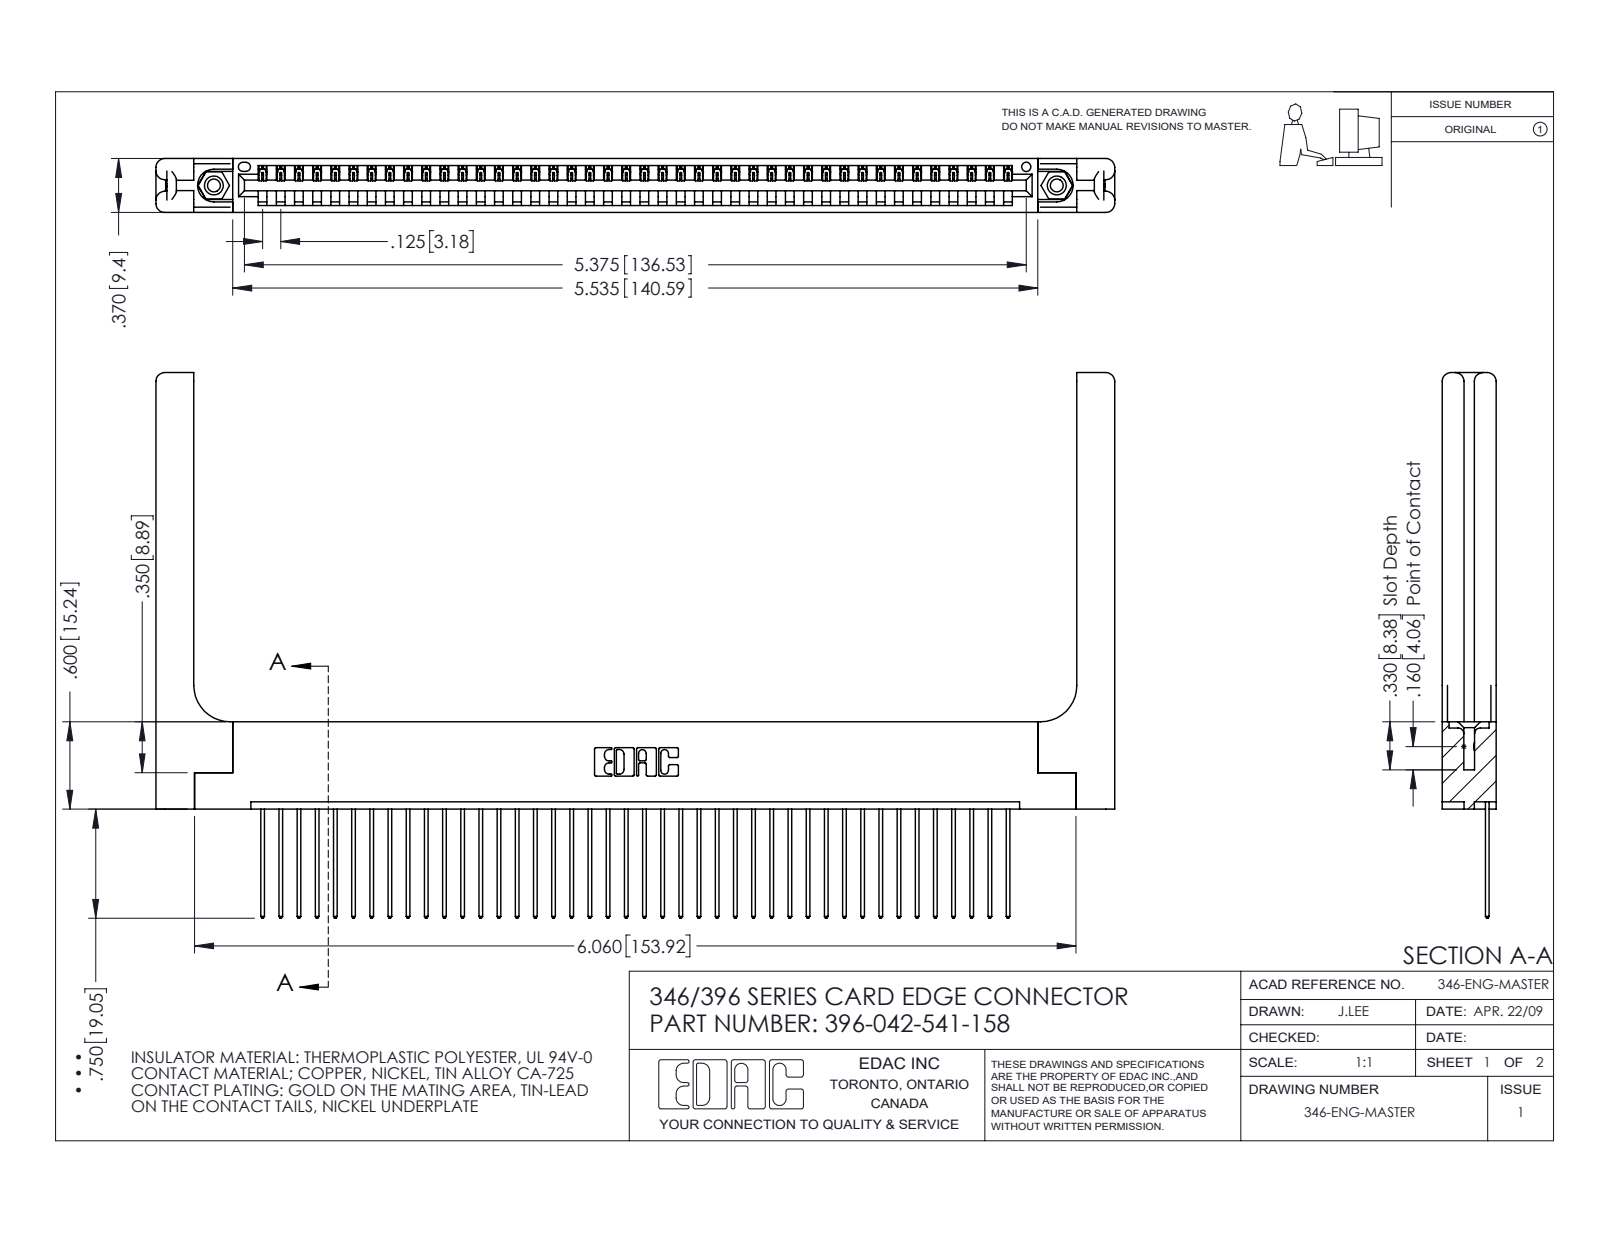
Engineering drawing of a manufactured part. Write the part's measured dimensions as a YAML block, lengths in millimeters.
part_name: "396-042-541-158; 345-250-001_345-250-001-102; 345-292-001_345-293-141; 346 Part_Flush Mounting Lugs - 0.156 Dia-TH (+1 more)"
step_written_by: "SolidWorks 2016 (CONFIG_CONTROL_DESIGN)"
units: millimeters
bodies: {solids: 47, faces: 2814, planar: 1904, cylindrical: 850, other: 60}
overall_size: [167.4, 95.3, 9.4]
volume: 23680
surface_area: 26200
round_holes:
  - {diameter: 2.3, count: 2}
  - {diameter: 3.2, count: 2}
  - {diameter: 4, count: 2}
  - {diameter: 1.6, count: 1}
round_bosses_or_shafts:
  - {diameter: 3.9, count: 2}
partial_cylinders:
  - {radius: 0.2, count: 84}
  - {radius: 0.3, count: 84}
  - {radius: 0.3, count: 22}
  - {radius: 1.5, count: 16}
  - {radius: 0.2, count: 6}
  - {radius: 0.8, count: 6}
  - {radius: 0.7, count: 3}
  - {radius: 0.8, count: 2}
face_to_face_distances: [9.4, 1.2, 8.2, 1.8, 3.8, 3.8, 7.6, 0.6, 6.4, 5.6]
hole_center_spacings: [6.2, 141.9, 147.2]
